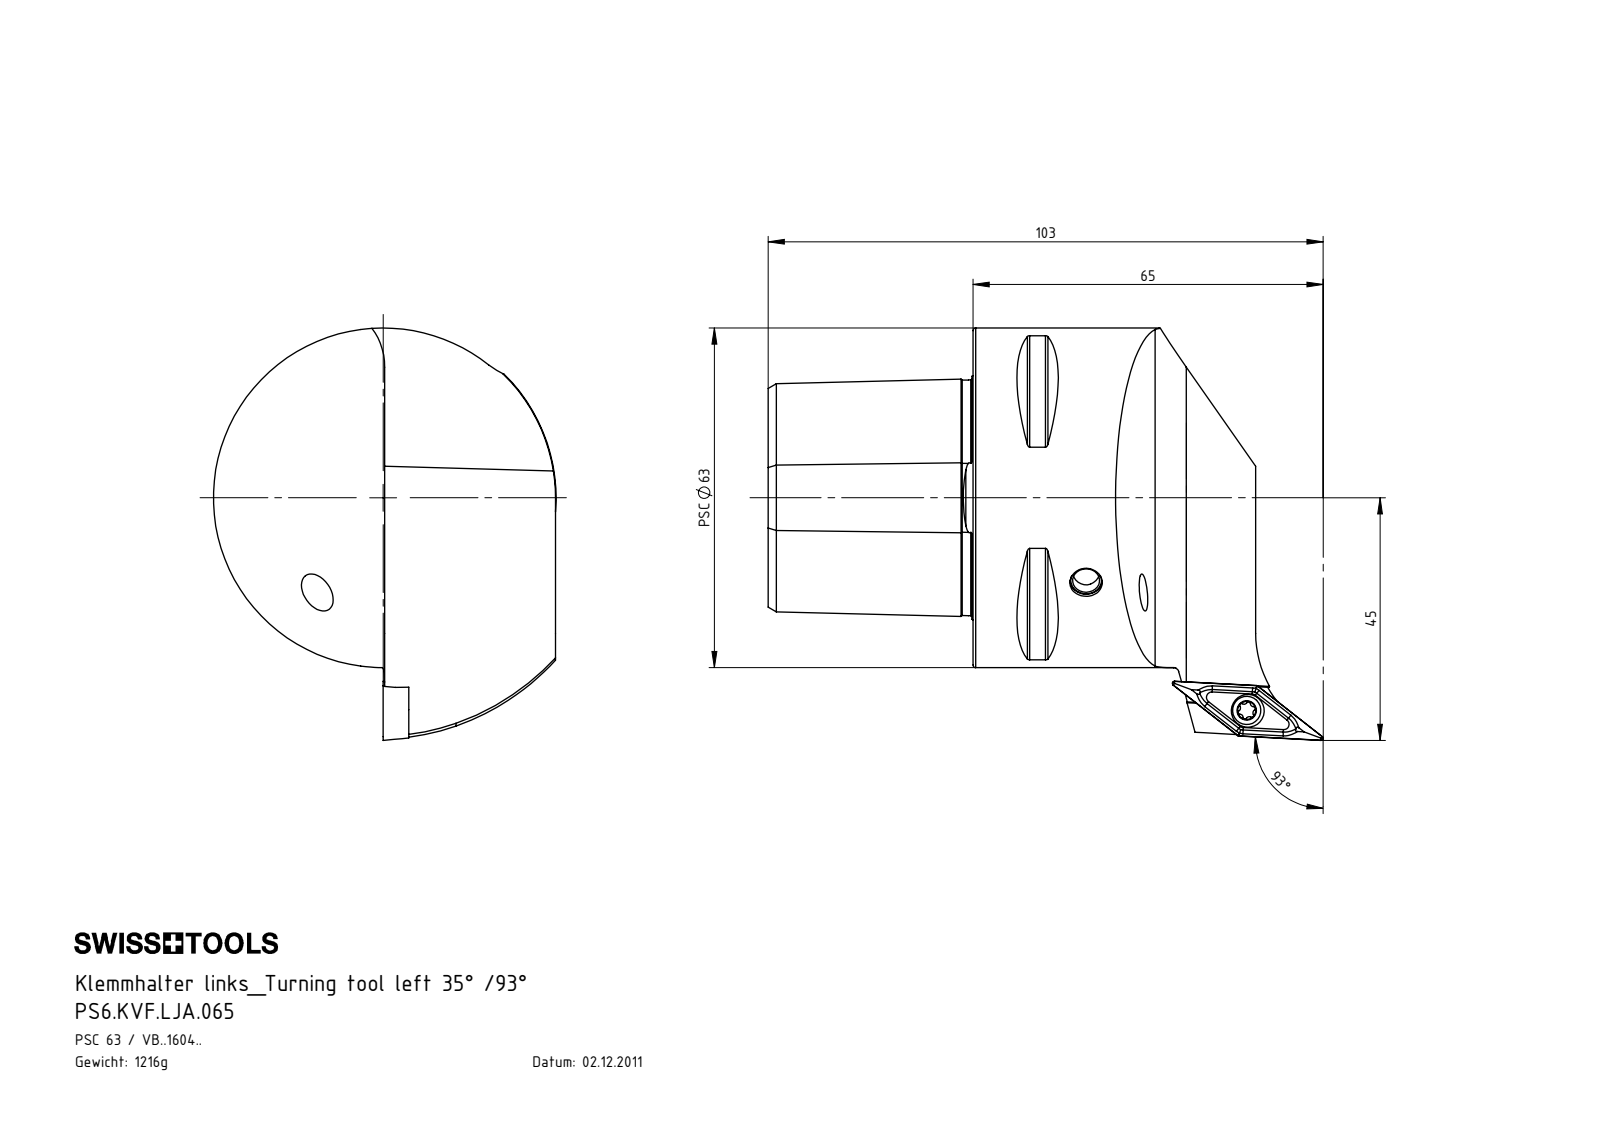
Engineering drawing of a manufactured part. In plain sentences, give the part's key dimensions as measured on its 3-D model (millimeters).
The part is named "WCB-ER2.001.009_A; VBMT160404; PS6.KVF.LJA.065; KVT_MB_600_060 (+1 more)". Its 3-D file was written by "SolidWorks 2017 (AUTOMOTIVE_DESIGN)". It is 5 solids with 275 faces: 57 planar, 69 cylindrical and 149 other. Overall it measures 103 by 76.5 by 63.61 millimeters. Its volume is 152 700 cubic millimeters and its surface area 27 674 square millimeters. Round holes: 2 of diameter 5, 1 of diameter 3.3, 1 of diameter 4, 1 of diameter 4.4, 1 of diameter 6.1, 1 of diameter 8.1, 1 of diameter 18, 1 of diameter 28, 1 of diameter 32. Round bosses or shafts: 1 of diameter 63, 1 of diameter 6, 1 of diameter 5.25, 1 of diameter 4. Partial cylindrical surfaces (rounded edges, fillets, slot ends): 8 of radius 0.5, 6 of radius 0.34, 6 of radius 0.59, 2 of radius 0.15, 2 of radius 6, 2 of radius 32, 1 of radius 11. The main face-to-face distances are 38, 24.88, 27, 11, 4.46, 55.8, 27.24, 31.7, 37.8, 10.8. The hole center spacings are 27.5, 55.33, 55.53, 77.15, 77.37.
